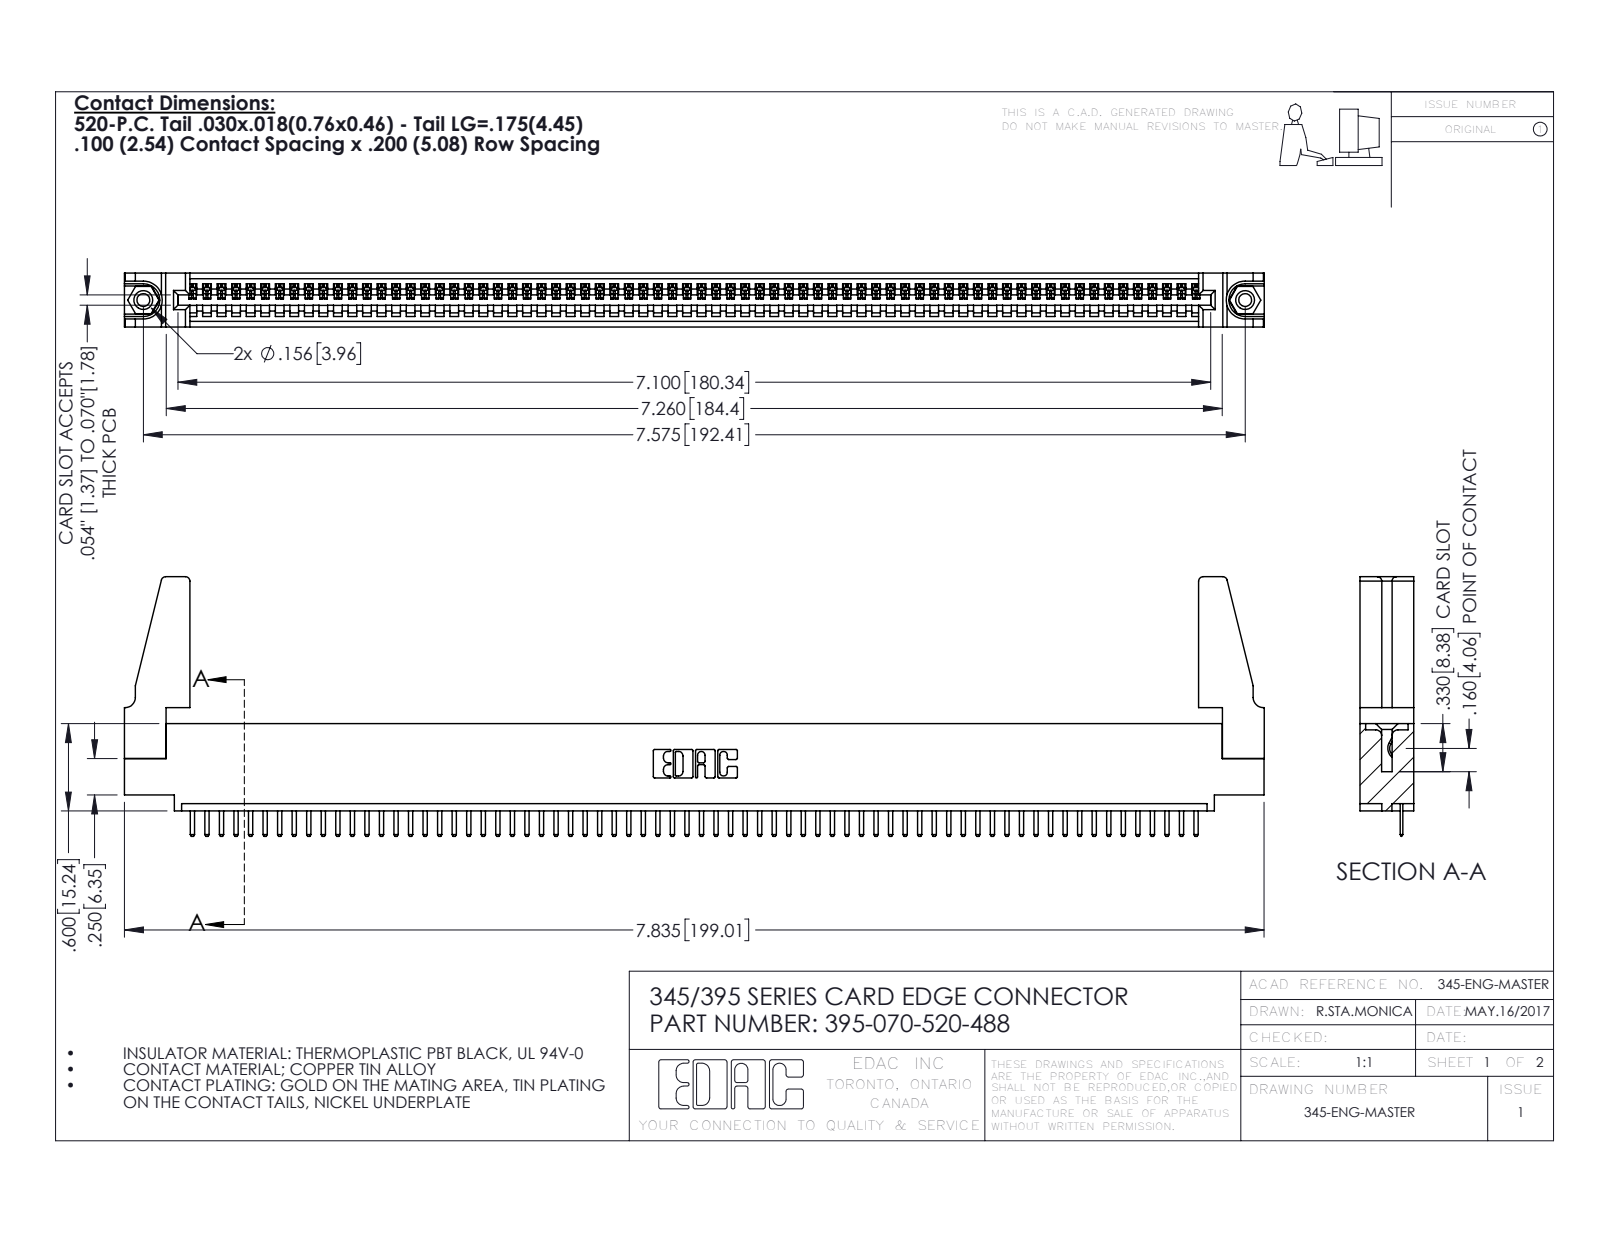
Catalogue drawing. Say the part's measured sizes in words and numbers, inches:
The part is named "345-250-001_345-250-001-102; 345-292-001_345-293-120; 395-070-520-488; 345-220-078_345-220-088 (+1 more)". Its 3-D file was written by "SolidWorks 2016 (CONFIG_CONTROL_DESIGN)". It is 75 solids with 4594 faces: 3096 planar, 1482 cylindrical and 16 other. Overall it measures 7.836 by 1.785 by 0.37 inches. Its volume is 1.349 cubic inches and its surface area 43.39 square inches. Round holes: 2 of diameter 0.089, 2 of diameter 0.125, 2 of diameter 0.156, 1 of diameter 0.064. Round bosses or shafts: 2 of diameter 0.155. Partial cylindrical surfaces (rounded edges, fillets, slot ends): 142 of radius 0.01, 140 of radius 0.006, 22 of radius 0.01, 8 of radius 0.03, 6 of radius 0.007, 6 of radius 0.031, 3 of radius 0.026, 2 of radius 0.031. The main face-to-face distances are 0.072, 0.298, 0.37, 0.2, 0.098, 0.272, 0.025, 0.225, 0.072, 0.149. The hole center spacings are 0.27, 7.339, 7.575.
